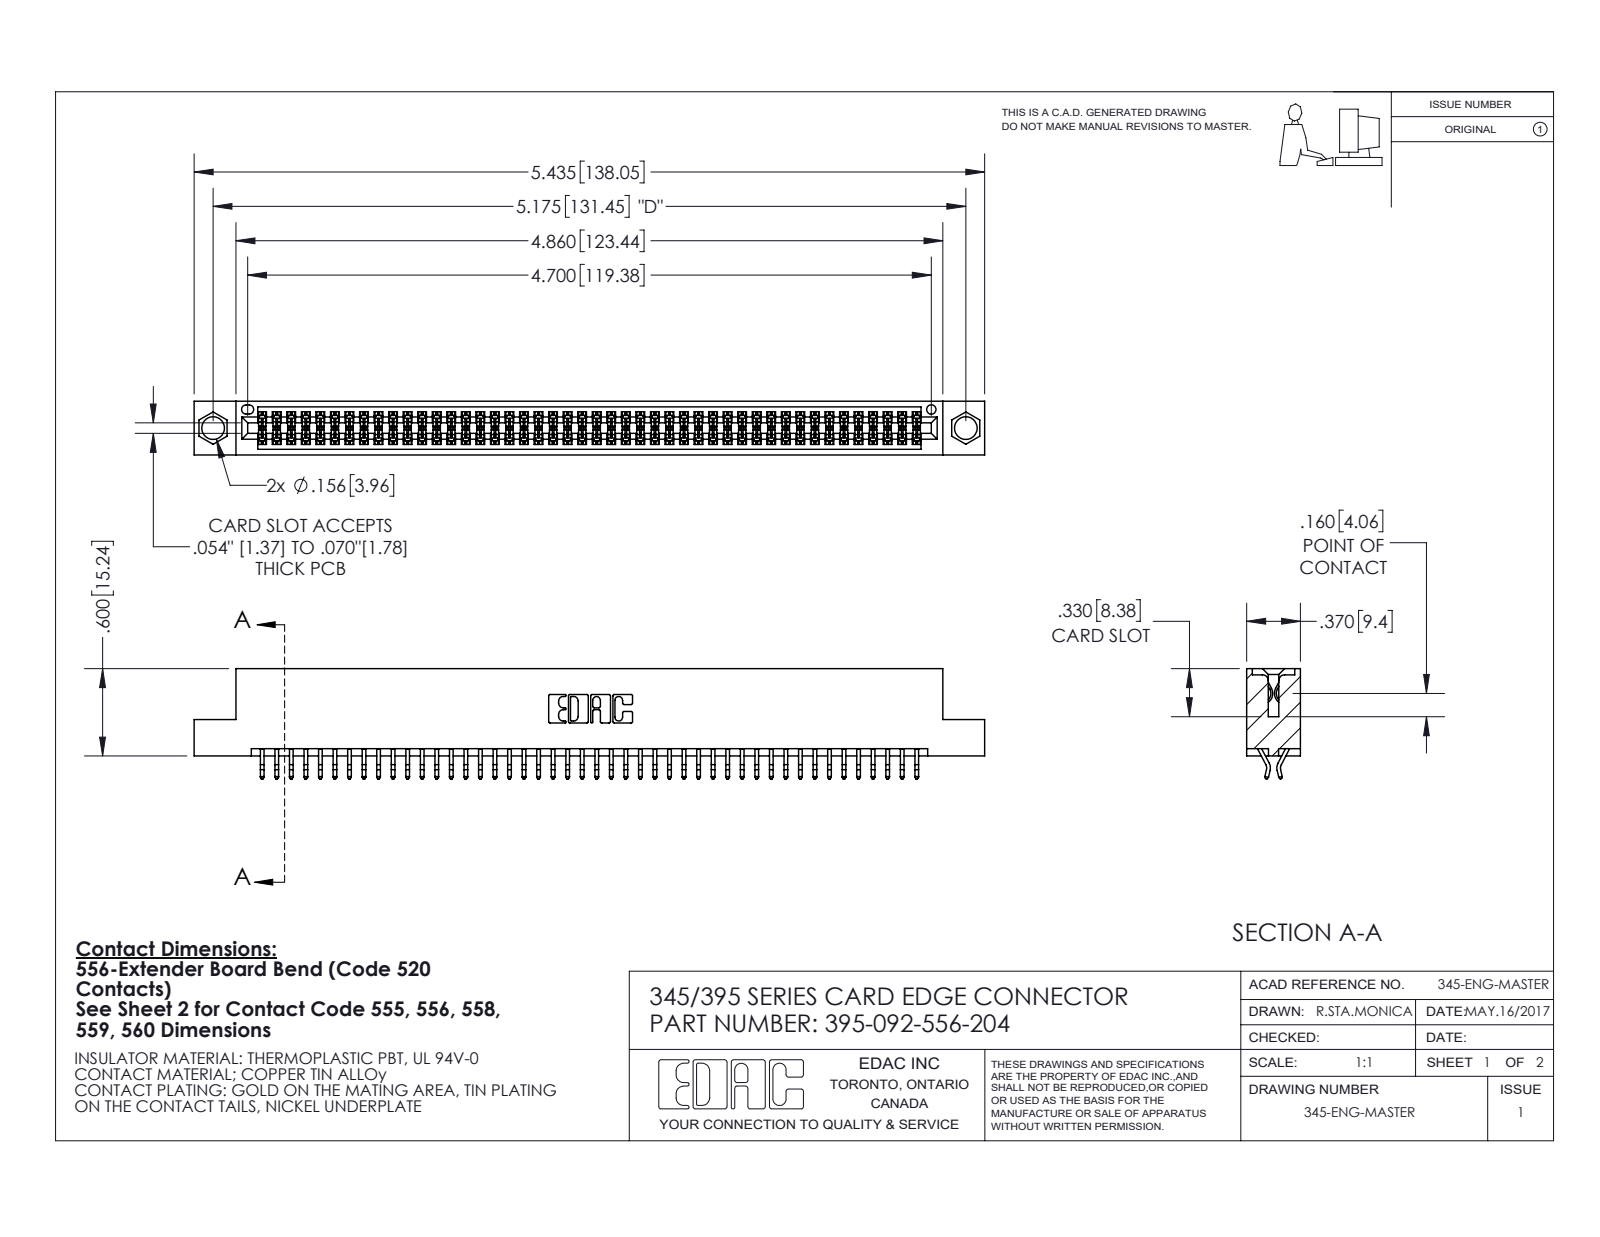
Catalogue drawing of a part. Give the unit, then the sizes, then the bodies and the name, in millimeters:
Units: millimetres
Overall size (bounding box): 138 × 19.2 × 9.4
Round holes (diameter × count): ⌀4 ×2, ⌀1.6 ×1
Partial cylindrical surfaces — rounded edges, fillets, slot ends (radius × count): R0.2 ×184, R0.3 ×22, R0.2 ×6, R0.8 ×6, R0.7 ×3, R0.3 ×2, R0.4 ×2, R0.5 ×2
Main face-to-face distances: 7.6, 1.8, 9.4, 5.1, 0.6, 2.5, 6.9, 5.7, 4.4, 3.8
Hole centre spacings: 6.9, 125.5, 131.4
Volume: 13 300 mm³ · Surface area: 19 560 mm²
Bodies: 93 solids, 5292 faces (3498 planar, 1794 cylindrical, 0 other)
Part name (STEP PRODUCT): 395-092-556-204; 345 Part_Flush Mounting Lugs - 0.156 Dia-TI; 345-292-001_556 Tail
STEP written by: SolidWorks 2020 (CONFIG_CONTROL_DESIGN)
